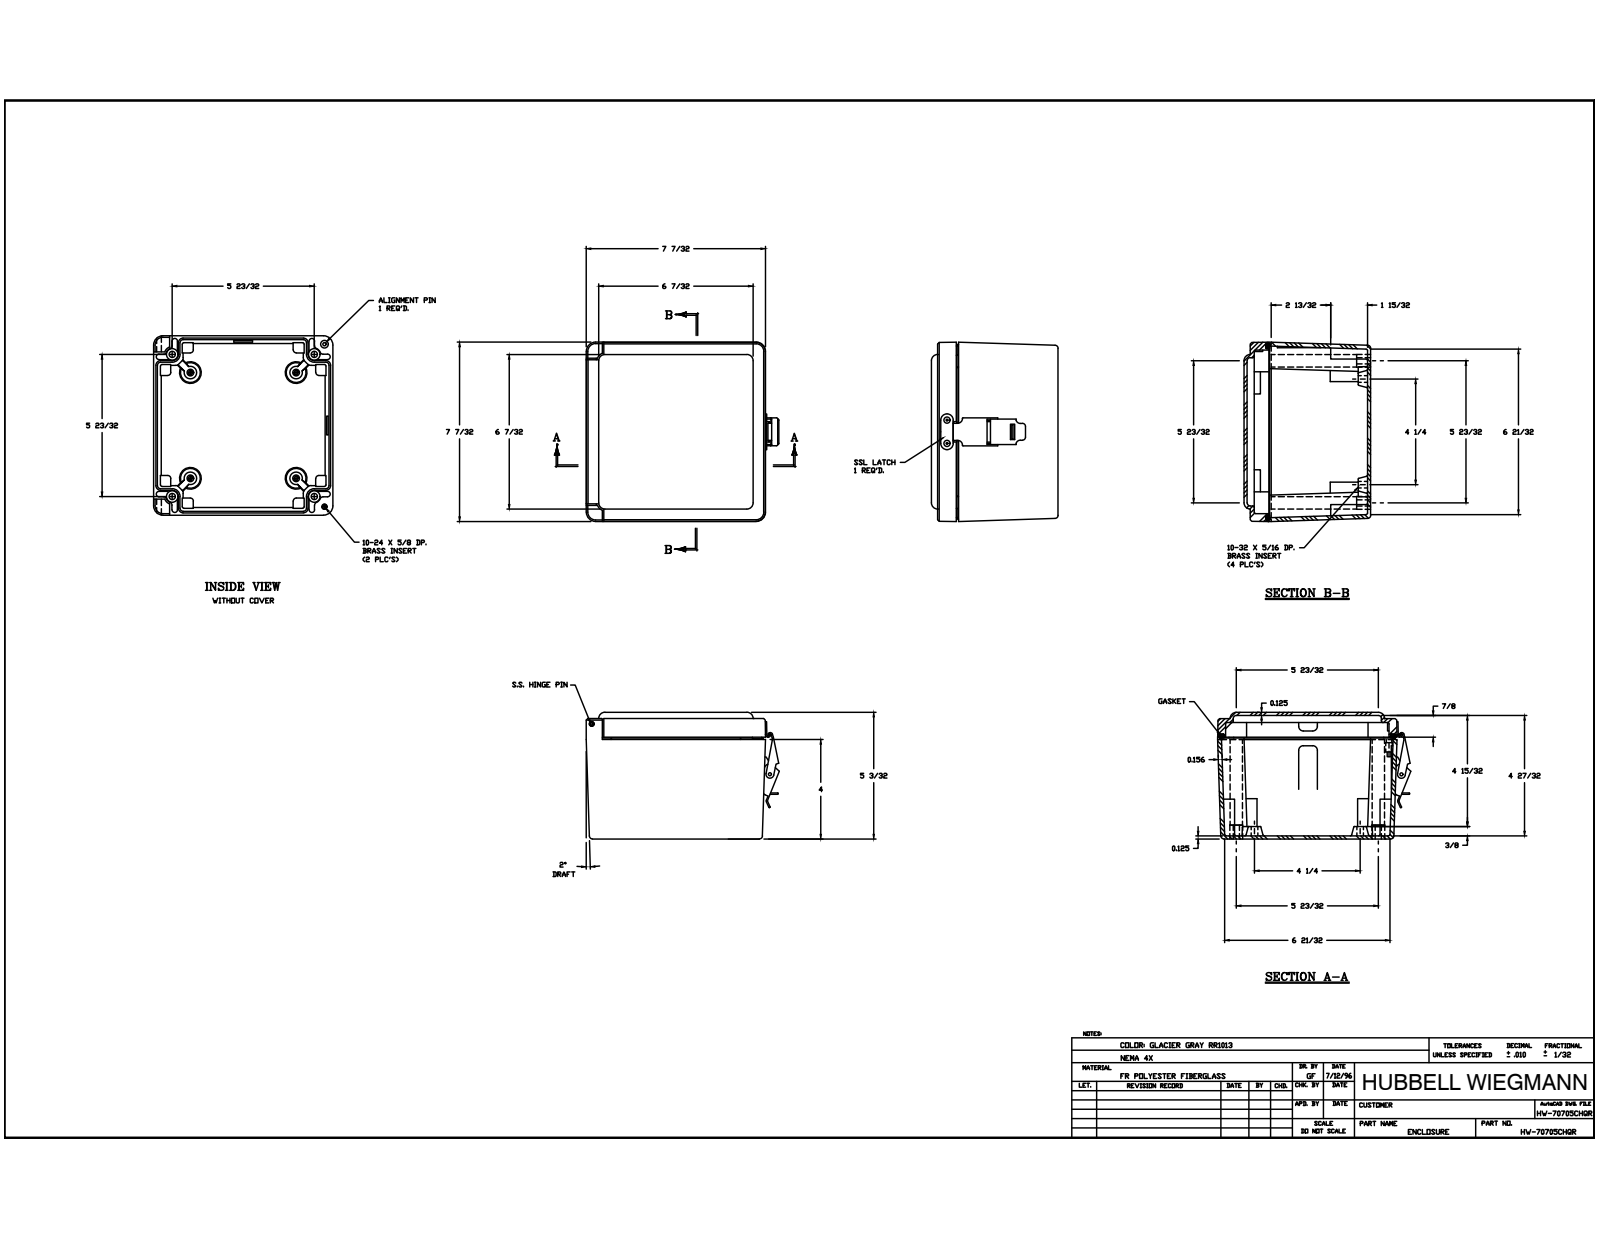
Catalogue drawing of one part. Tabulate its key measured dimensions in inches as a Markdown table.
| quantity | value |
| --- | --- |
| part name | WP707HPLBOX; 0.3125-18 X 0.563 DP BRASS INSERT; 10-32 X0.3125 DP BRASS INSERT; 10-24 X 0.625 DP BRASS INSERT (+8 more) |
| STEP written by | Autodesk Inventor 2014 (AUTOMOTIVE_DESIGN) |
| units | inches |
| bodies | 30 solids, 1086 faces (421 planar, 341 cylindrical, 324 other) |
| overall size | 7.818 × 7.22 × 5.094 |
| volume | 50.22 in³ |
| surface area | 567 in² |
| round holes (diameter × count) | 0.281 × 6, 0.104 × 4, 0.14 × 4, 0.156 × 4, 0.313 × 4, 0.531 × 4, 0.096 × 2, 0.098 × 2, 0.13 × 2, 0.135 × 2, 0.145 × 2, 0.156 × 2 |
| round bosses / shafts (diameter × count) | 0.375 × 2, 0.371 × 2, 0.234 × 2, 0.178 × 2, 0.095 × 2, 0.088 × 2, 0.3 × 1, 0.299 × 1 |
| partial cylindrical surfaces (radius × count) | 0.031 × 52, 0.063 × 30, 0.125 × 30, 0.045 × 8, 0.059 × 8, 0.375 × 8, 0.03 × 6, 0.187 × 6 |
| main face-to-face distances | 0.125, 0.186, 4.969, 5.094, 4.844, 0.125, 0.75, 4.844, 4.719, 0.25 |
| hole center spacings | 5.04, 1.039, 4.251, 5.511, 5.72, 6.14, 7.051, 0.528 |
